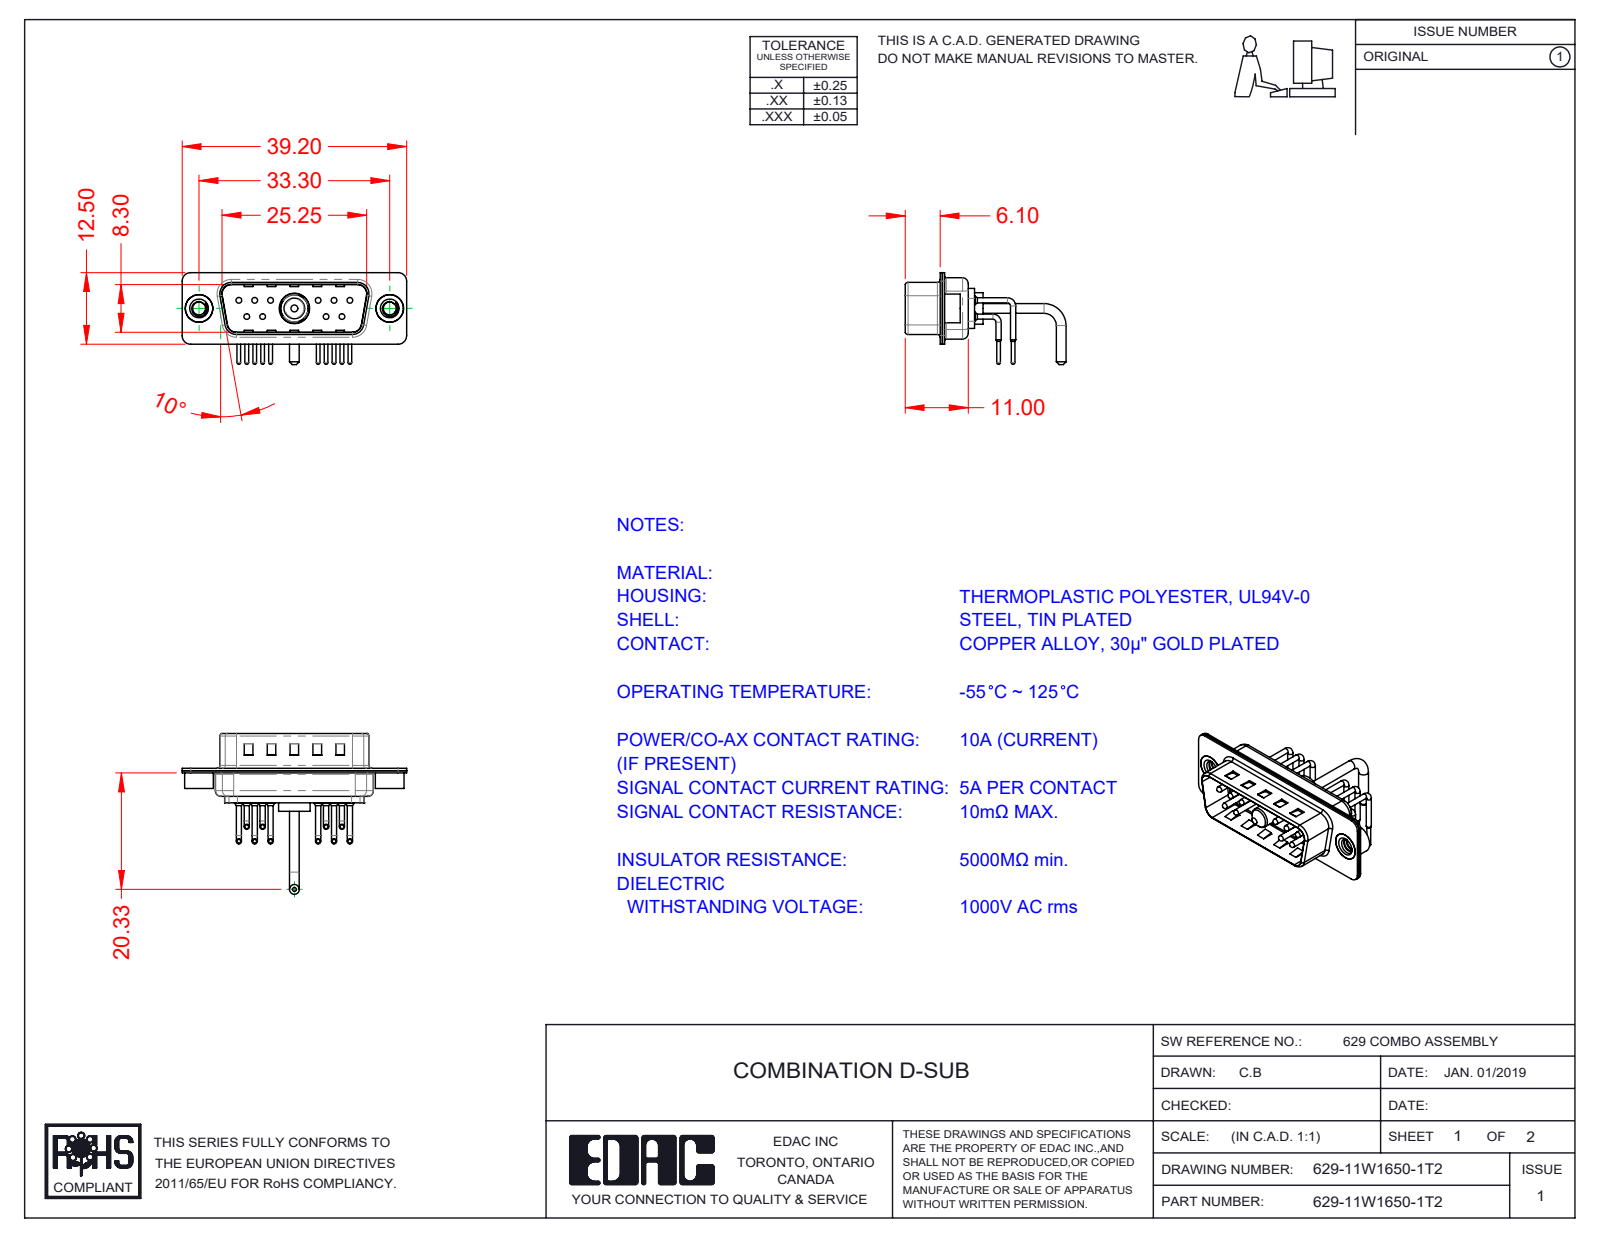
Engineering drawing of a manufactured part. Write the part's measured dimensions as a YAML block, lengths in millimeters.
part_name: "629Combo Threaded Rivet_2; 629-11W1650-1T2; Power Pin_Ext 10A RA; 629Combo Contact Row 1 (+4 more)"
step_written_by: "SolidWorks 2020 (CONFIG_CONTROL_DESIGN)"
units: millimeters
bodies: {solids: 17, faces: 1496, planar: 798, cylindrical: 518, other: 180}
overall_size: [39.2, 28.08, 16.05]
volume: 2022
surface_area: 5221
round_holes:
  - {diameter: 0.75, count: 10}
  - {diameter: 1.6, count: 10}
  - {diameter: 2, count: 10}
  - {diameter: 2.26, count: 2}
  - {diameter: 4, count: 2}
  - {diameter: 4.8, count: 2}
  - {diameter: 4.85, count: 1}
  - {diameter: 5.3, count: 1}
round_bosses_or_shafts:
  - {diameter: 0.9, count: 20}
  - {diameter: 1.5, count: 10}
  - {diameter: 1, count: 10}
  - {diameter: 0.65, count: 10}
  - {diameter: 5, count: 2}
  - {diameter: 4.9, count: 2}
  - {diameter: 1.7, count: 2}
  - {diameter: 5.5, count: 1}
partial_cylinders:
  - {radius: 1.5, count: 16}
  - {radius: 2, count: 12}
  - {radius: 1.01, count: 10}
  - {radius: 0.5, count: 8}
  - {radius: 1.6, count: 8}
  - {radius: 1, count: 7}
  - {radius: 0.25, count: 4}
  - {radius: 0.6, count: 4}
face_to_face_distances: [0.4, 0.8, 9.5, 9.1, 8.7, 9.9, 5.6, 0.75, 1.2, 0.35]
hole_center_spacings: [3.16, 2.77, 13.85, 11.08, 16.62, 5.03, 5.04, 5.54]
